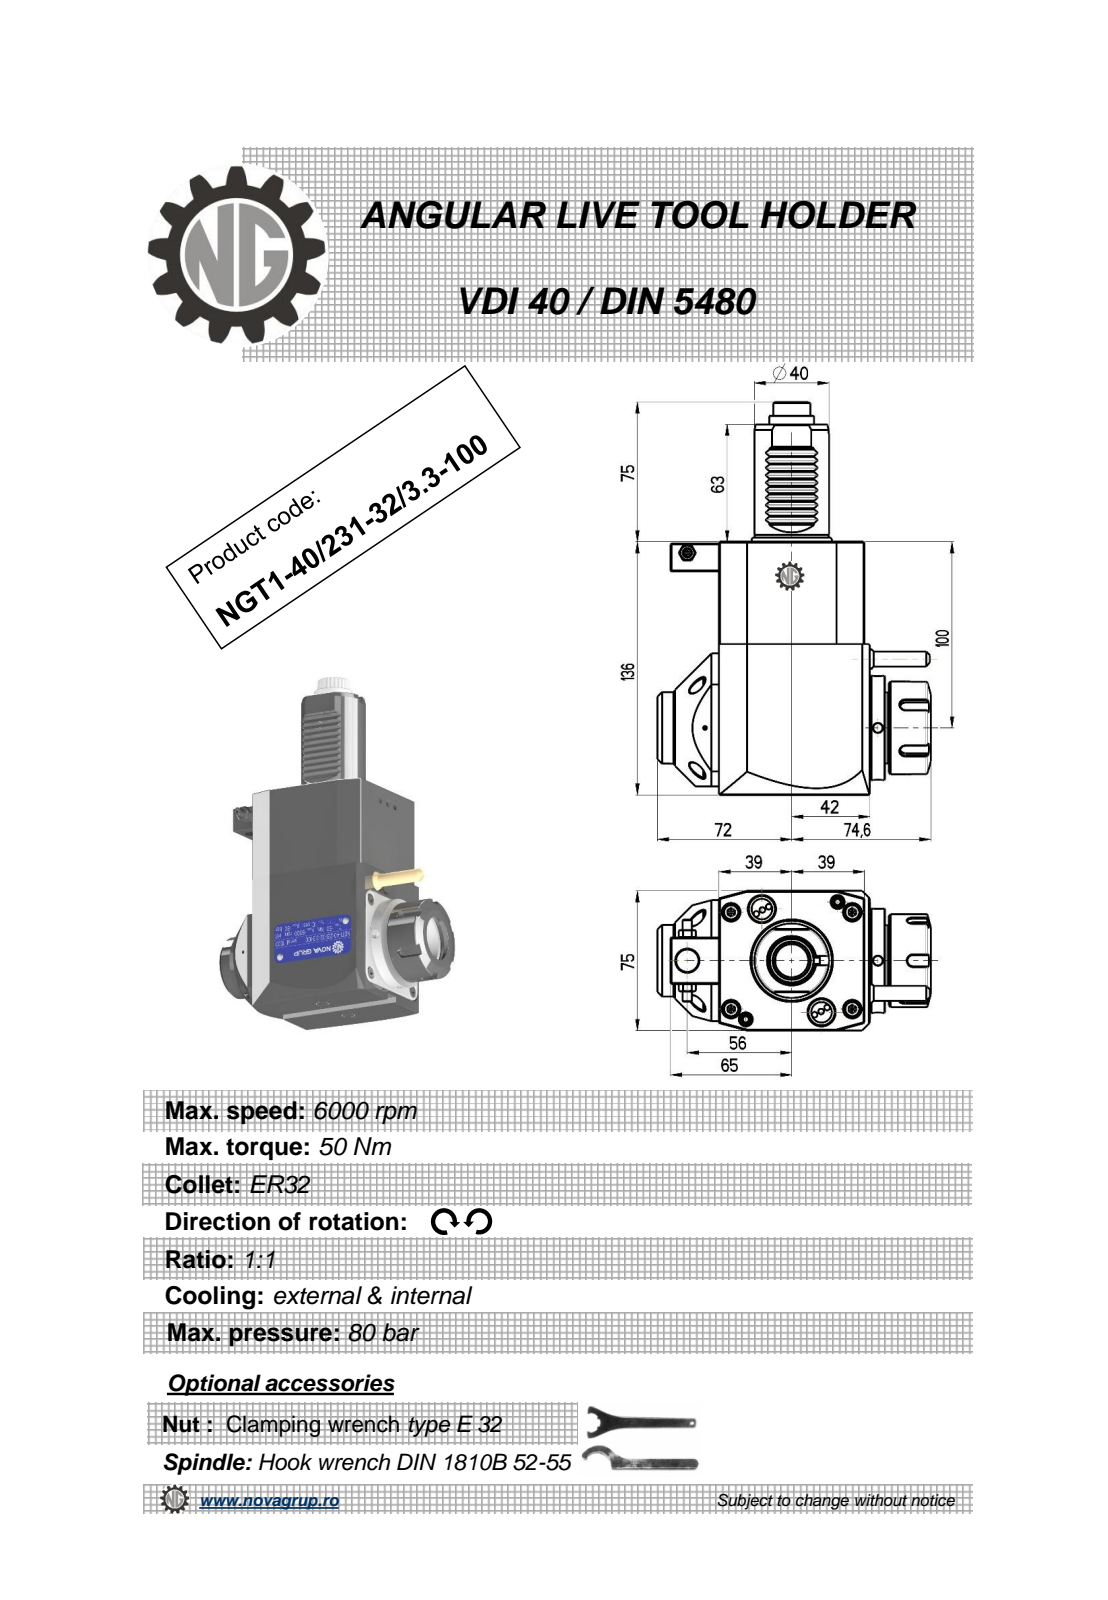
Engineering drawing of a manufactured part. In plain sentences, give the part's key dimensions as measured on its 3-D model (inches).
The part is named "NGT1_40_231_32_3_3_100". Its 3-D file was written by "PRO/ENGINEER BY PARAMETRIC TECHNOLOGY CORPORATION, 2010280 (CONFIG_CONTROL_DESIGN)". It is 1 solid with 627 faces: 229 planar, 233 cylindrical and 165 other. Overall it measures 8.307 by 5.772 by 2.953 inches. Its volume is 62.49 cubic inches and its surface area 122.6 square inches. Round holes: 3 of diameter 0.197, 1 of diameter 0.118, 1 of diameter 0.165, 1 of diameter 0.374, 1 of diameter 0.472, 1 of diameter 1.063. Round bosses or shafts: 1 of diameter 2.205, 1 of diameter 1.969, 1 of diameter 1.693, 1 of diameter 1.575, 1 of diameter 1.516, 1 of diameter 0.945, 1 of diameter 0.441, 1 of diameter 0.353. Partial cylindrical surfaces (rounded edges, fillets, slot ends): 48 of radius 0.082, 20 of radius 0.012, 12 of radius 0.01, 6 of radius 0.009, 5 of radius 0.118, 1 of radius 0.357, 1 of radius 0.391, 1 of radius 0.591. The main face-to-face distances are 2.953, 5.354, 3.071, 3.189, 0.118, 3.342, 0.295, 0.02, 3.181, 0.11. The hole center spacings are 1.611, 2.254, 3.602, 4.026, 5.468.
